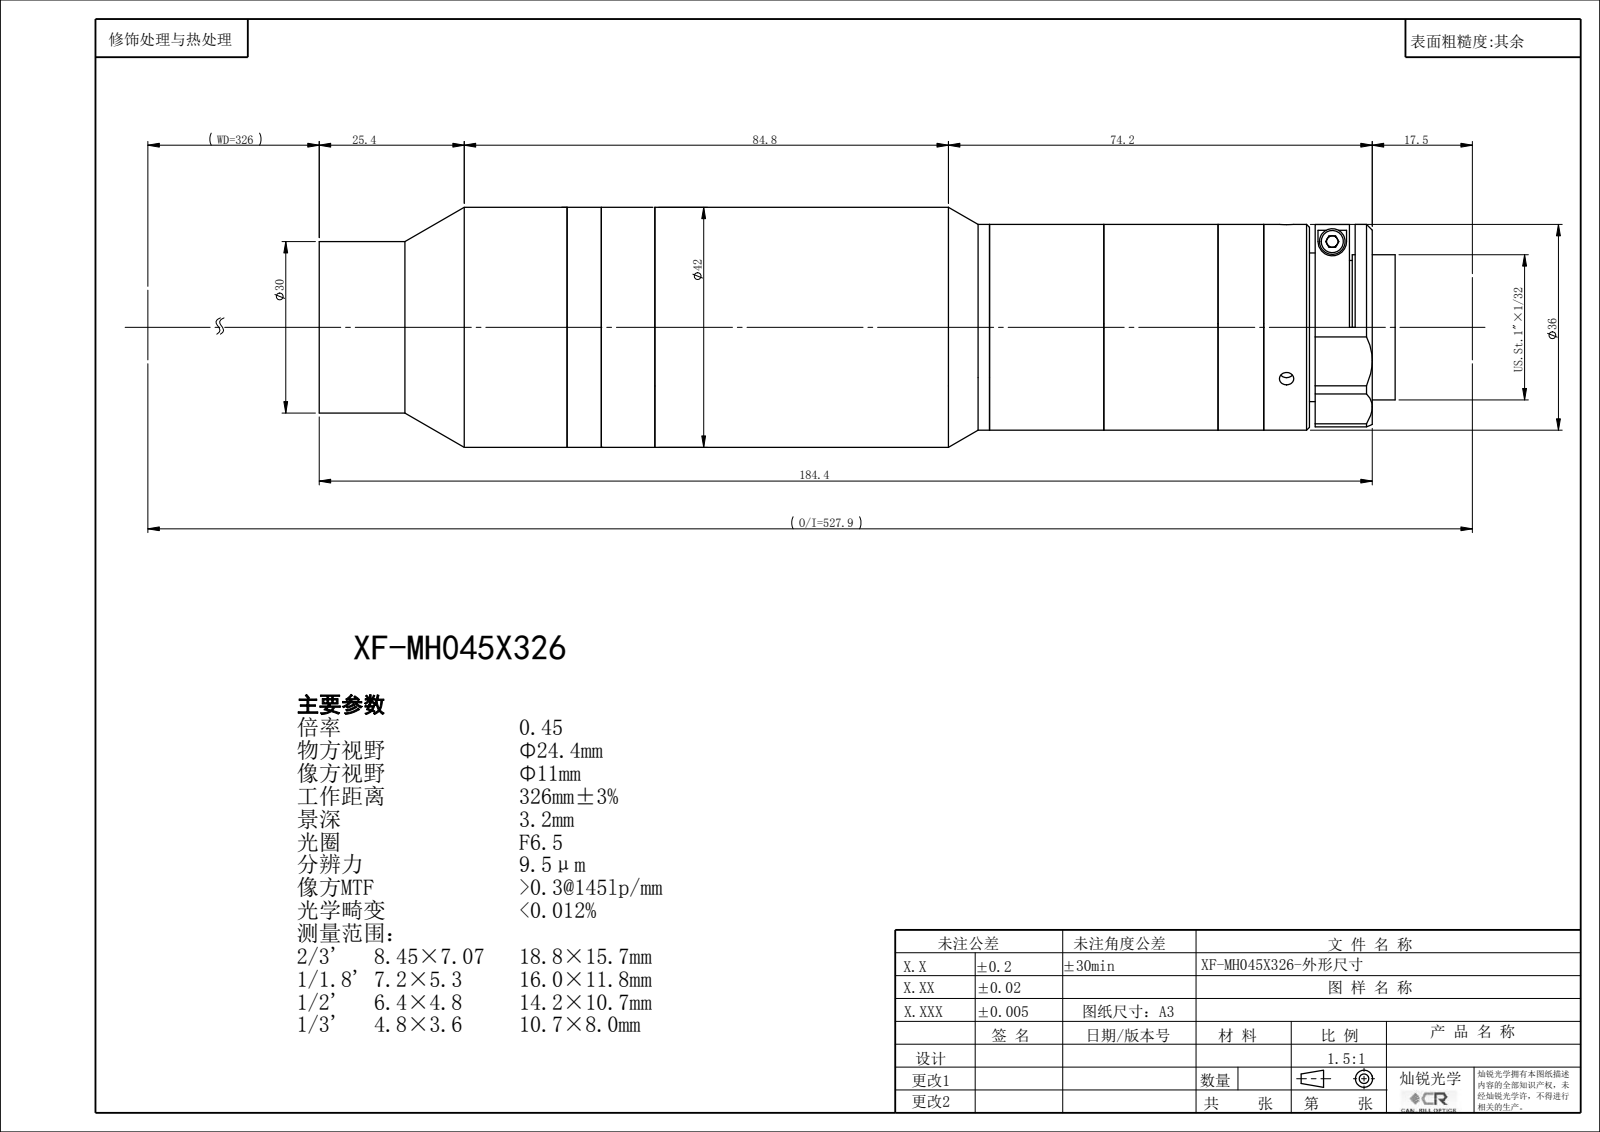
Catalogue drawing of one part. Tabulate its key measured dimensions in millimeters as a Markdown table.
| quantity | value |
| --- | --- |
| part name | XF-MH045X326 |
| STEP written by | SolidWorks 2022 (CONFIG_CONTROL_DESIGN) |
| units | millimeters |
| bodies | 0 solids, 132 faces (64 planar, 46 cylindrical, 22 other) |
| overall size | 188.65 × 42 × 42 |
| round holes (diameter × count) | 2.5 × 3, 22.4 × 1, 24 × 1, 26.4 × 1 |
| round bosses / shafts (diameter × count) | 42 × 1, 36 × 1, 34 × 1, 30 × 1, 25.4 × 1 |
| main face-to-face distances | 20, 1.5, 25.8, 27.3, 45.8, 47.3, 28, 8, 17.8, 19.3 |
